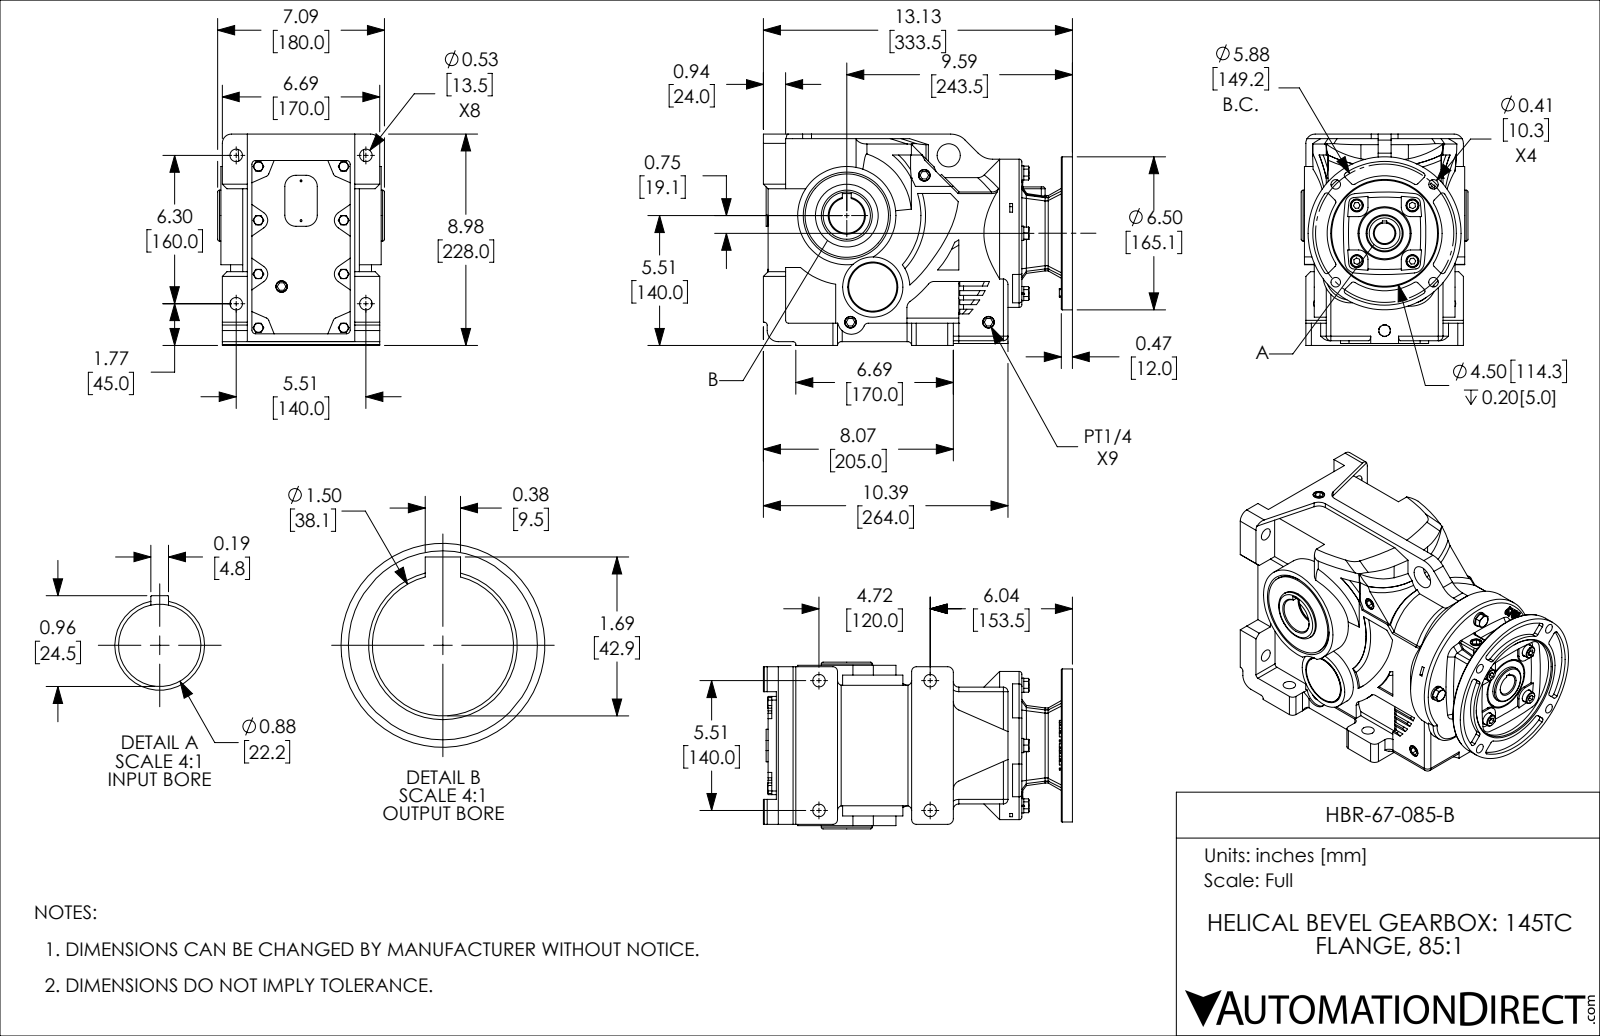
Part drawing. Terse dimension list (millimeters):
name: HBR-67-085-B
written by: SolidWorks 2018 (AUTOMOTIVE_DESIGN)
unit: mm
bodies: 1 solid, 1131 faces (598 planar, 268 cylindrical, 265 other)
size: 333.5 × 228 × 180
volume: 7 913 000 mm³; area: 412 300 mm²
holes: 8× ⌀13.5, 4× ⌀8.2, 4× ⌀9, 4× ⌀10.3, 4× ⌀14, 2× ⌀2, 1× ⌀22.2, 1× ⌀25, 1× ⌀28, 1× ⌀38.1, 1× ⌀40, 1× ⌀114.3
bosses: 4× ⌀15.4, 4× ⌀13, 4× ⌀8, 2× ⌀55, 1× ⌀165.1, 1× ⌀160, 1× ⌀106, 1× ⌀90
rounds: 20× R5, 19× R3, 15× R10, 12× R4, 7× R2, 5× R12, 4× R6, 4× R300
face distances: 5, 2, 24, 7, 1.5, 223, 126, 4, 3, 49.5
hole spacings: 54.2, 99.7, 32.1, 42.5, 46.1, 65, 74.6, 85.9
